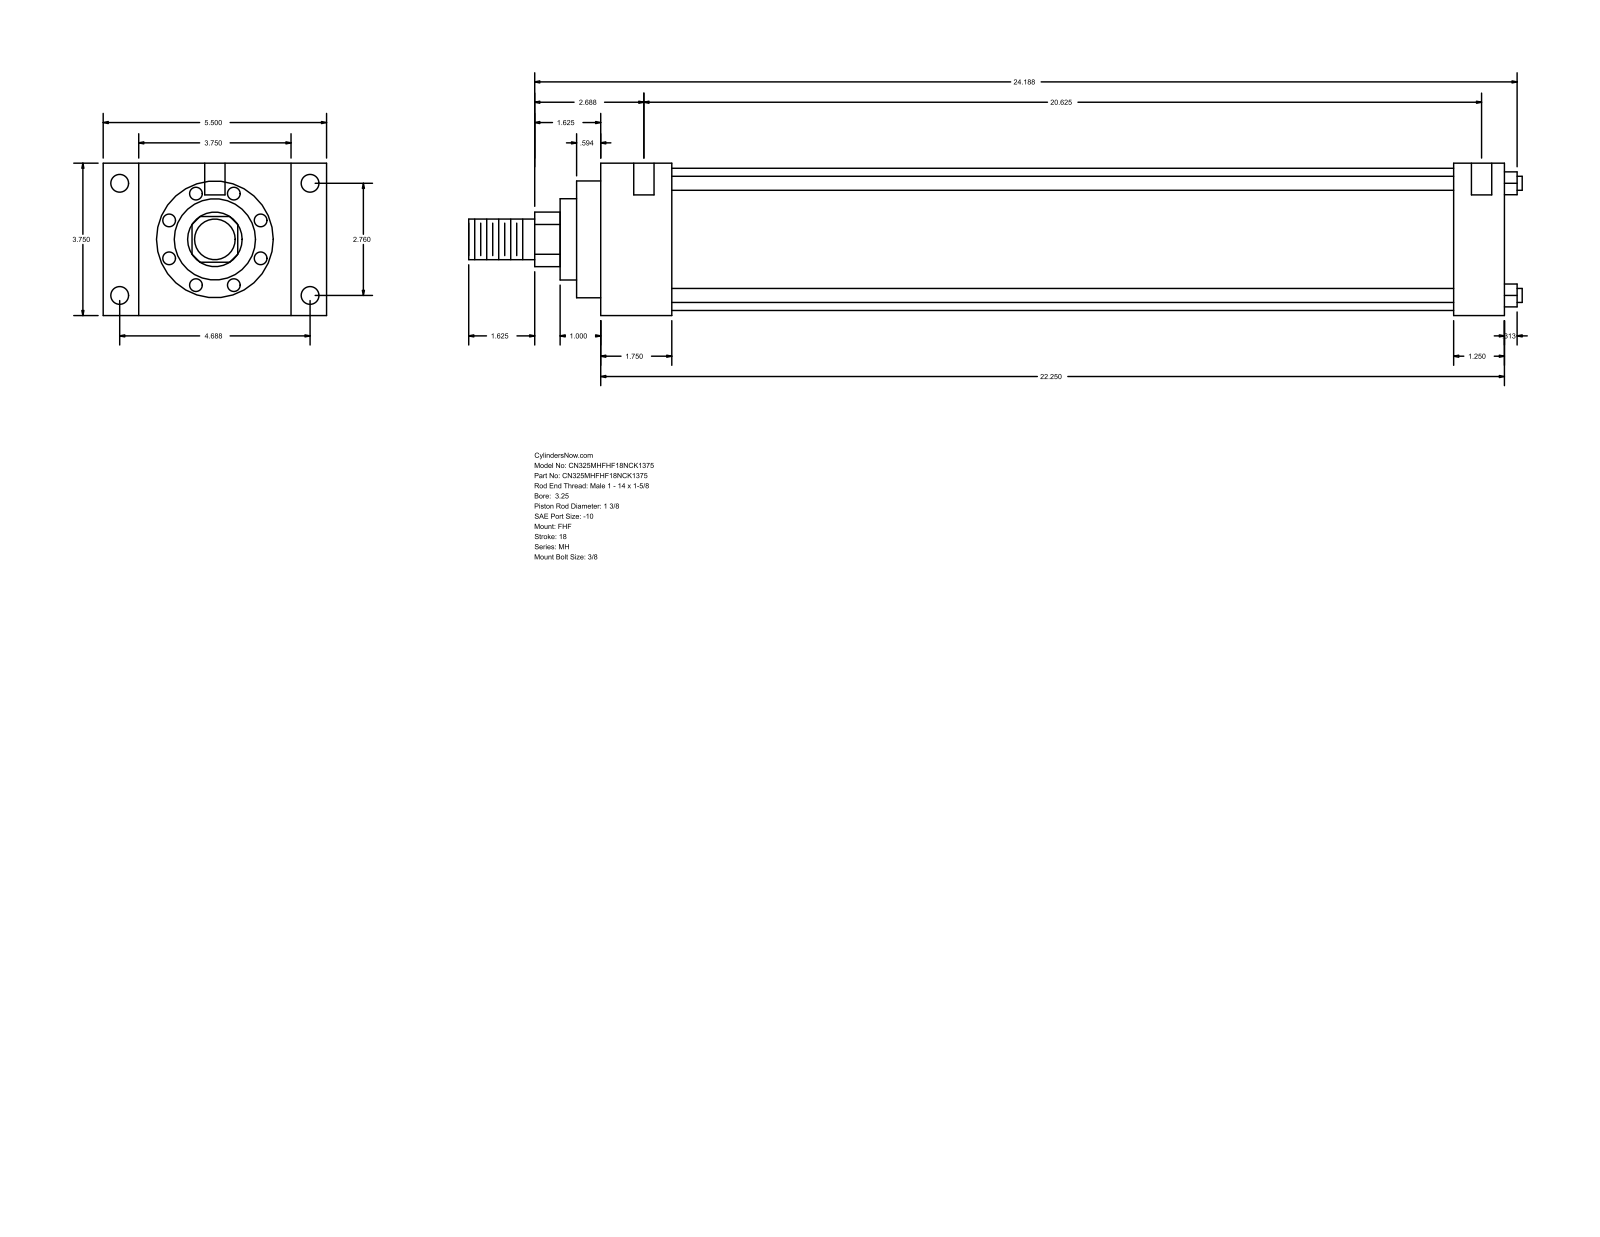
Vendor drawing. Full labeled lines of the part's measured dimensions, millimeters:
Part name (STEP PRODUCT): MH_FHF__0325_1.375
STEP written by: GSSL Pune (CONFIG_CONTROL_DESIGN)
Units: millimetres
Bodies: 0 solids, 90 faces (61 planar, 29 cylindrical, 0 other)
Overall size (bounding box): 658.81 × 139.7 × 95.25
Round holes (diameter × count): ⌀5.56 ×4, ⌀11.13 ×4, ⌀12.7 ×2
Round bosses / shafts (diameter × count): ⌀8.76 ×4, ⌀88.9 ×1, ⌀73.03 ×1, ⌀50.8 ×1, ⌀34.92 ×1, ⌀25.4 ×1
Partial cylindrical surfaces — rounded edges, fillets, slot ends (radius × count): R17.06 ×1
Main face-to-face distances: 95.24, 565.15, 44.45, 520.7, 22.23, 117.47, 139.7, 533.4, 488.95, 31.75
Hole centre spacings: 70.1, 119.06, 138.16, 530.23, 1.59, 4.76, 523.88, 525.47
